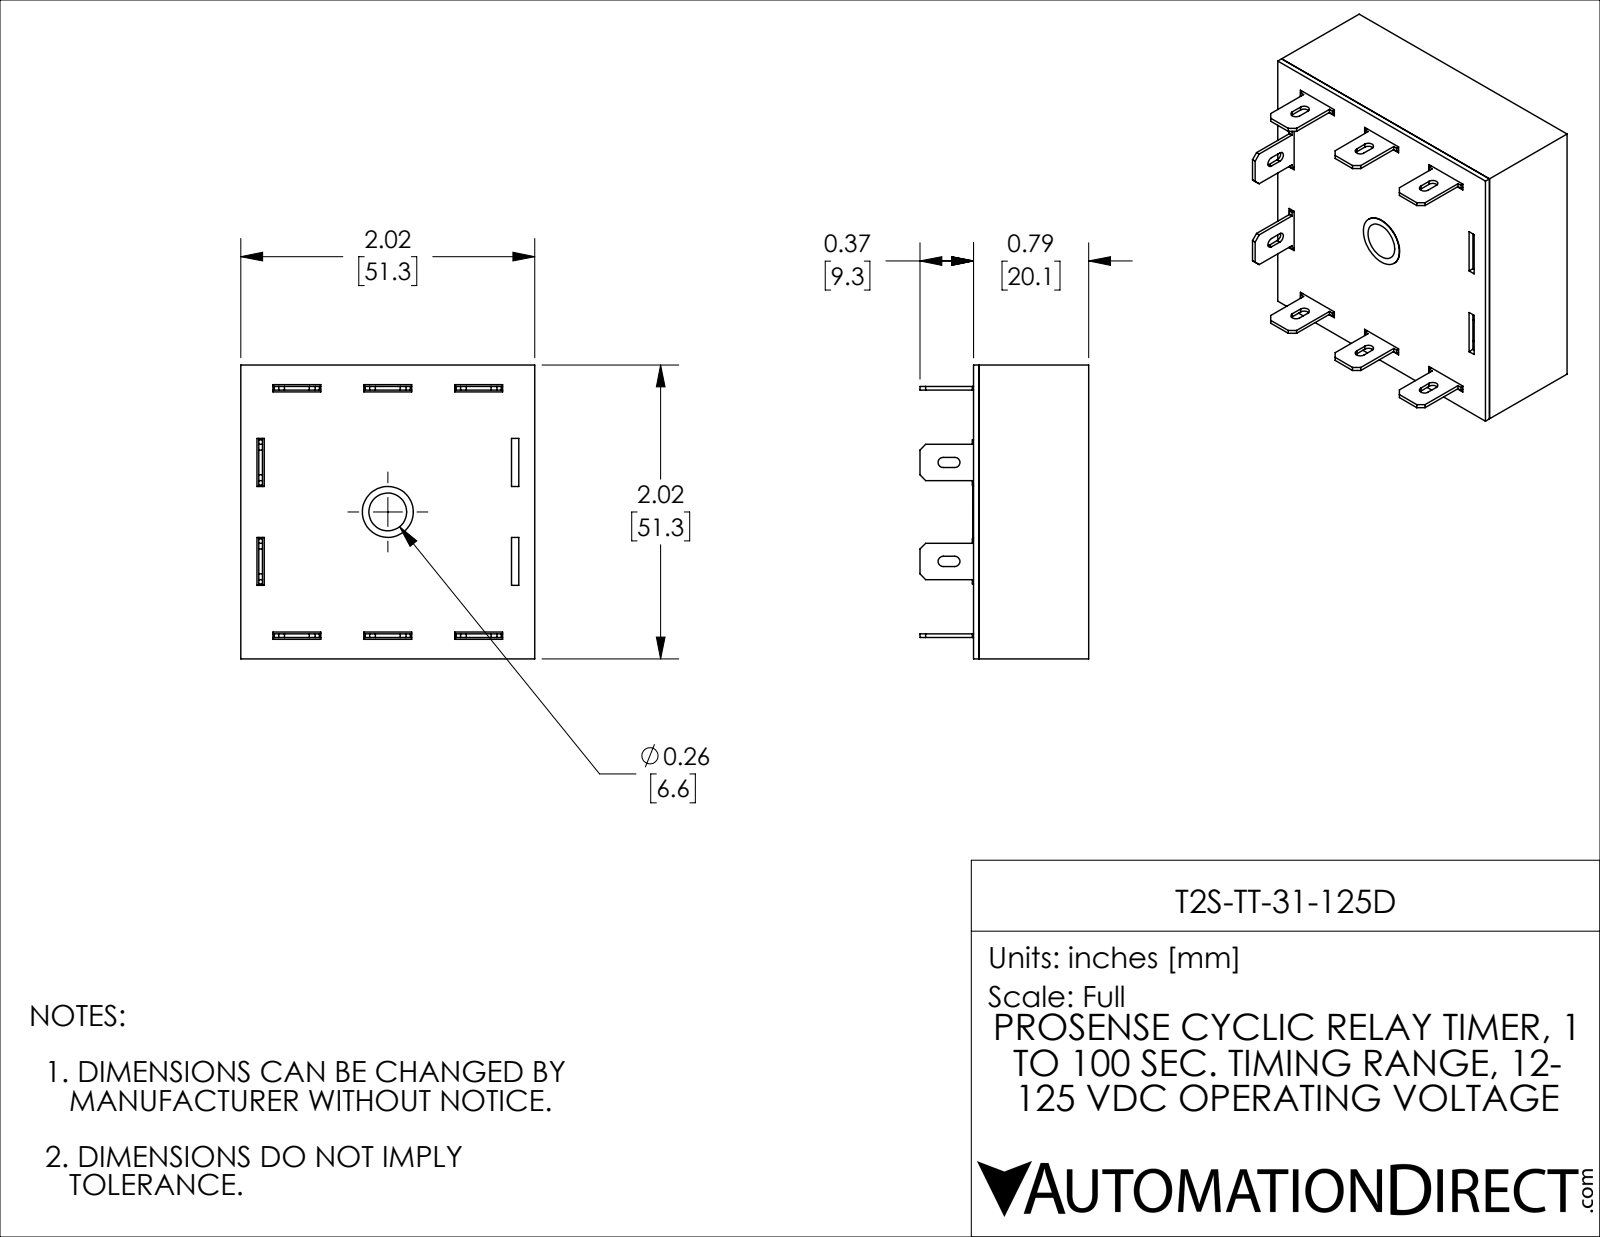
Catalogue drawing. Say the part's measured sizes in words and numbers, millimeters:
The part is named "T2S-TT-31-125D". Its 3-D file was written by "SolidWorks 2021 (CONFIG_CONTROL_DESIGN)". It is 10 solids with 256 faces: 234 planar, 20 cylindrical and 2 other. Overall it measures 51.31 by 51.31 by 29.46 millimeters. Its volume is 11 042 cubic millimeters and its surface area 22 819 square millimeters. Round holes: 1 of diameter 8.89. Partial cylindrical surfaces (rounded edges, fillets, slot ends): 10 of radius 0.89. The main face-to-face distances are 1.14, 50.16, 19.15, 20.12, 0.97, 18.01, 18.98, 51.3, 49.02, 3.74.
